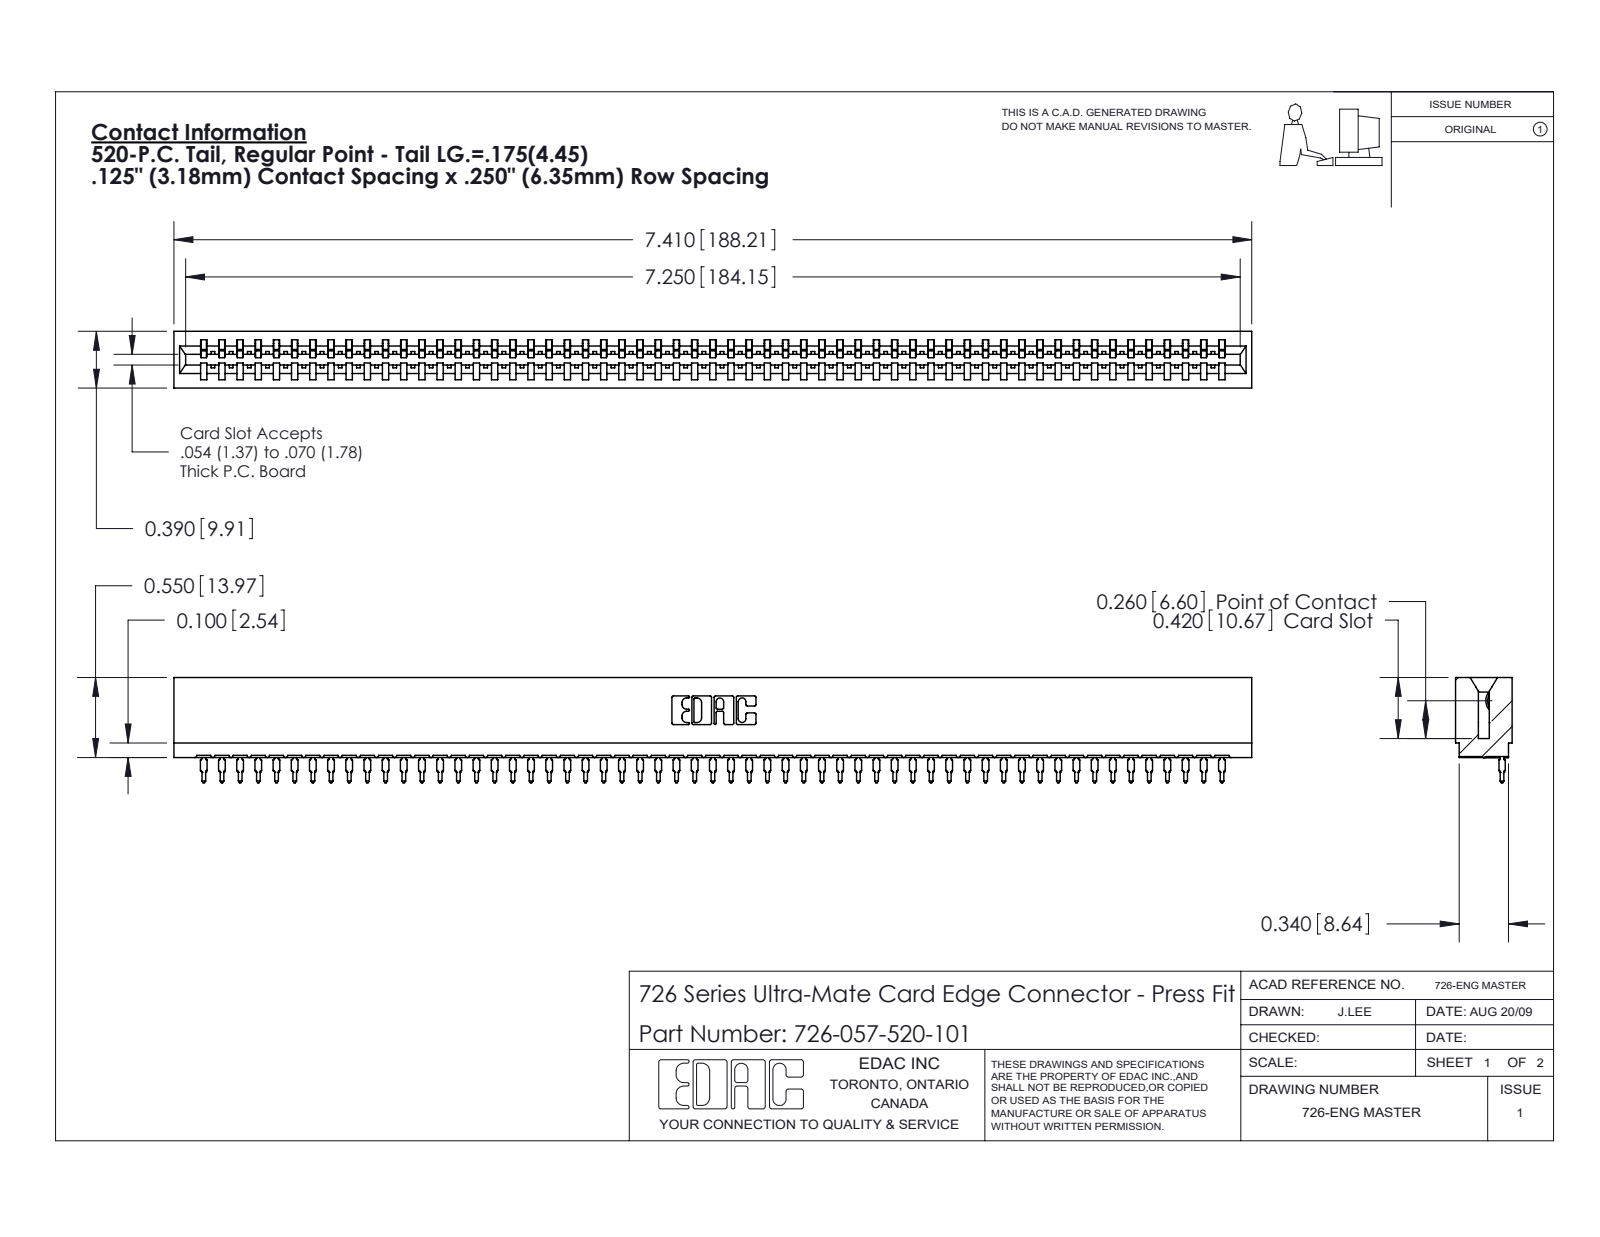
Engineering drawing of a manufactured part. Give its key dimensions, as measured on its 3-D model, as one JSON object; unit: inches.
{"part_name": "726 Part_.515 Slot Depth - 01; 726-057-520-101; 746-292-001_520", "step_written_by": "SolidWorks 2020 (CONFIG_CONTROL_DESIGN)", "units": "inches", "bodies": {"solids": 58, "faces": 6253, "planar": 3646, "cylindrical": 1125, "other": 1482}, "overall_size": [7.41, 0.724, 0.39], "volume_in3": 1.015, "surface_area_in2": 39.08, "partial_cylinders_radius": [[0.021, 114], [0.015, 58], [0.01, 22], [0.007, 6], [0.031, 6], [0.005, 4], [0.011, 4], [0.026, 3]], "face_to_face_distances": [0.057, 0.333, 0.39, 0.025, 0.307, 0.25, 0.275, 0.365, 0.032, 0.174]}
